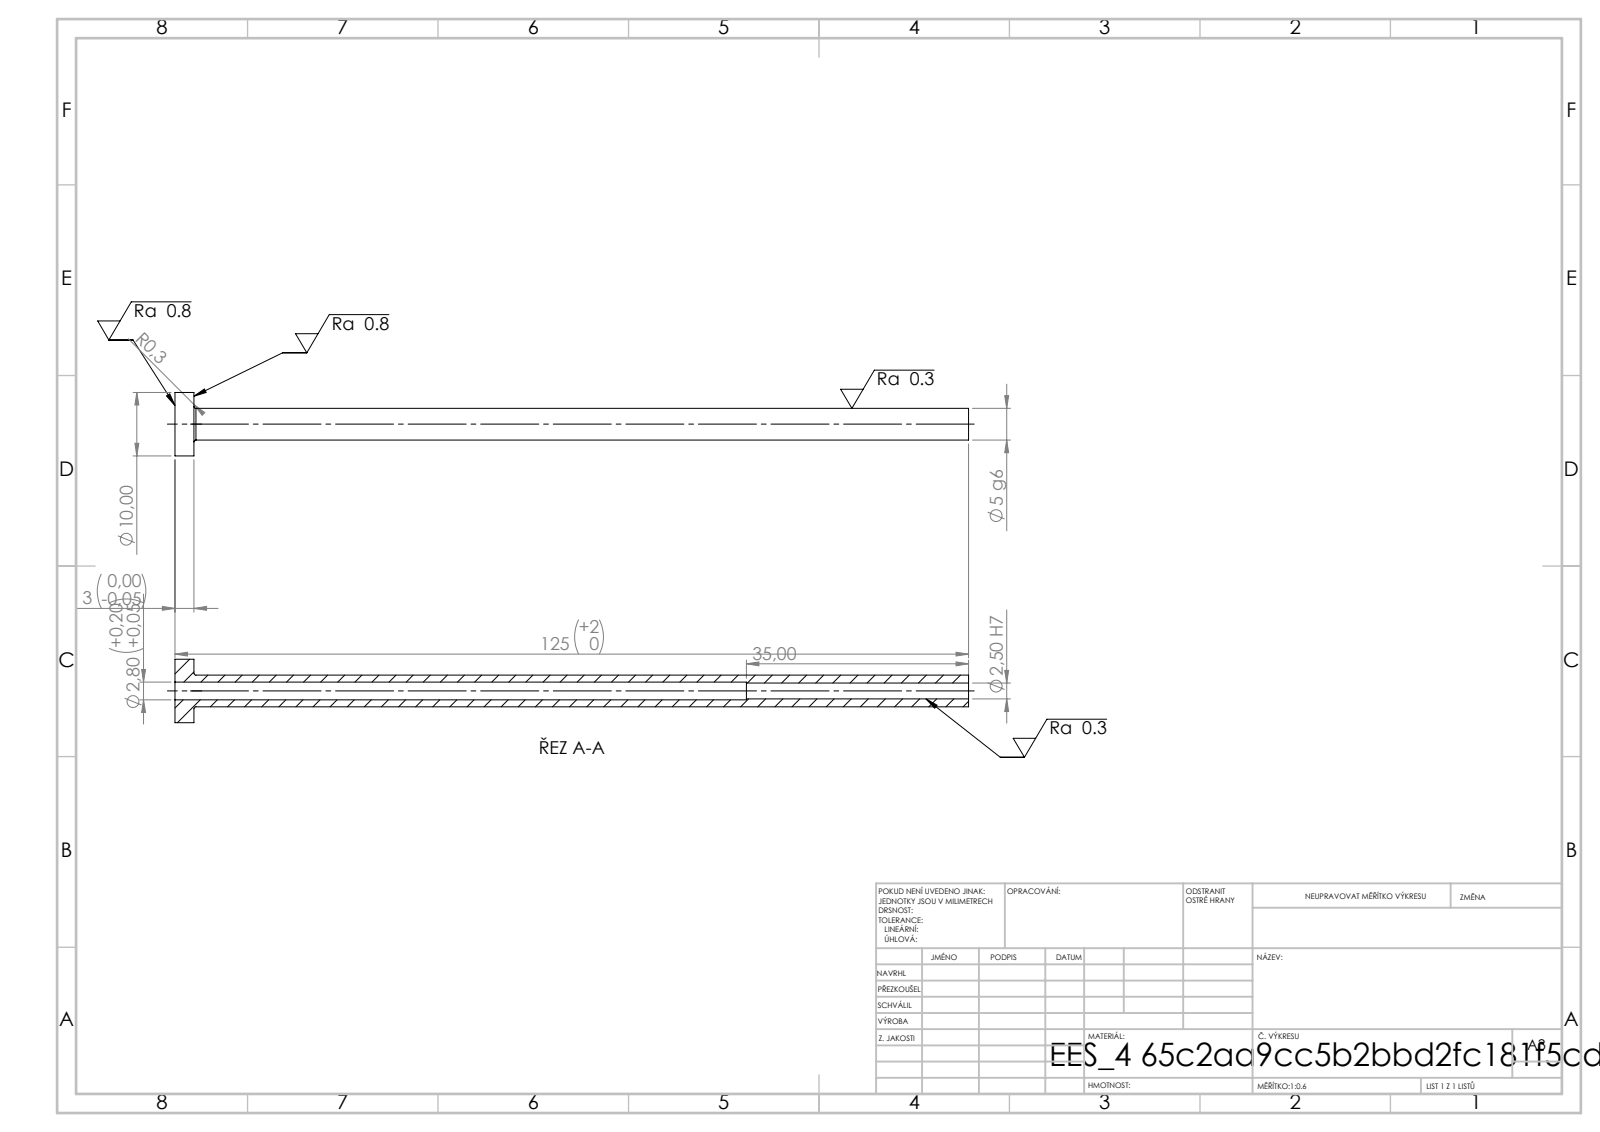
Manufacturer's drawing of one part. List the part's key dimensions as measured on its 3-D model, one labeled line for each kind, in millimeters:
STEP written by: SolidWorks 2019 (CONFIG_CONTROL_DESIGN)
Units: millimetres
Bodies: 1 solid, 14 faces (4 planar, 8 cylindrical, 2 other)
Overall size (bounding box): 125 × 10 × 10
Volume: 1 905 mm³ · Surface area: 3 222 mm²
Round holes (diameter × count): ⌀2.5 ×1, ⌀2.8 ×1
Round bosses / shafts (diameter × count): ⌀10 ×1, ⌀5 ×1
Main face-to-face distances: 3, 125, 122, 90, 87, 35
